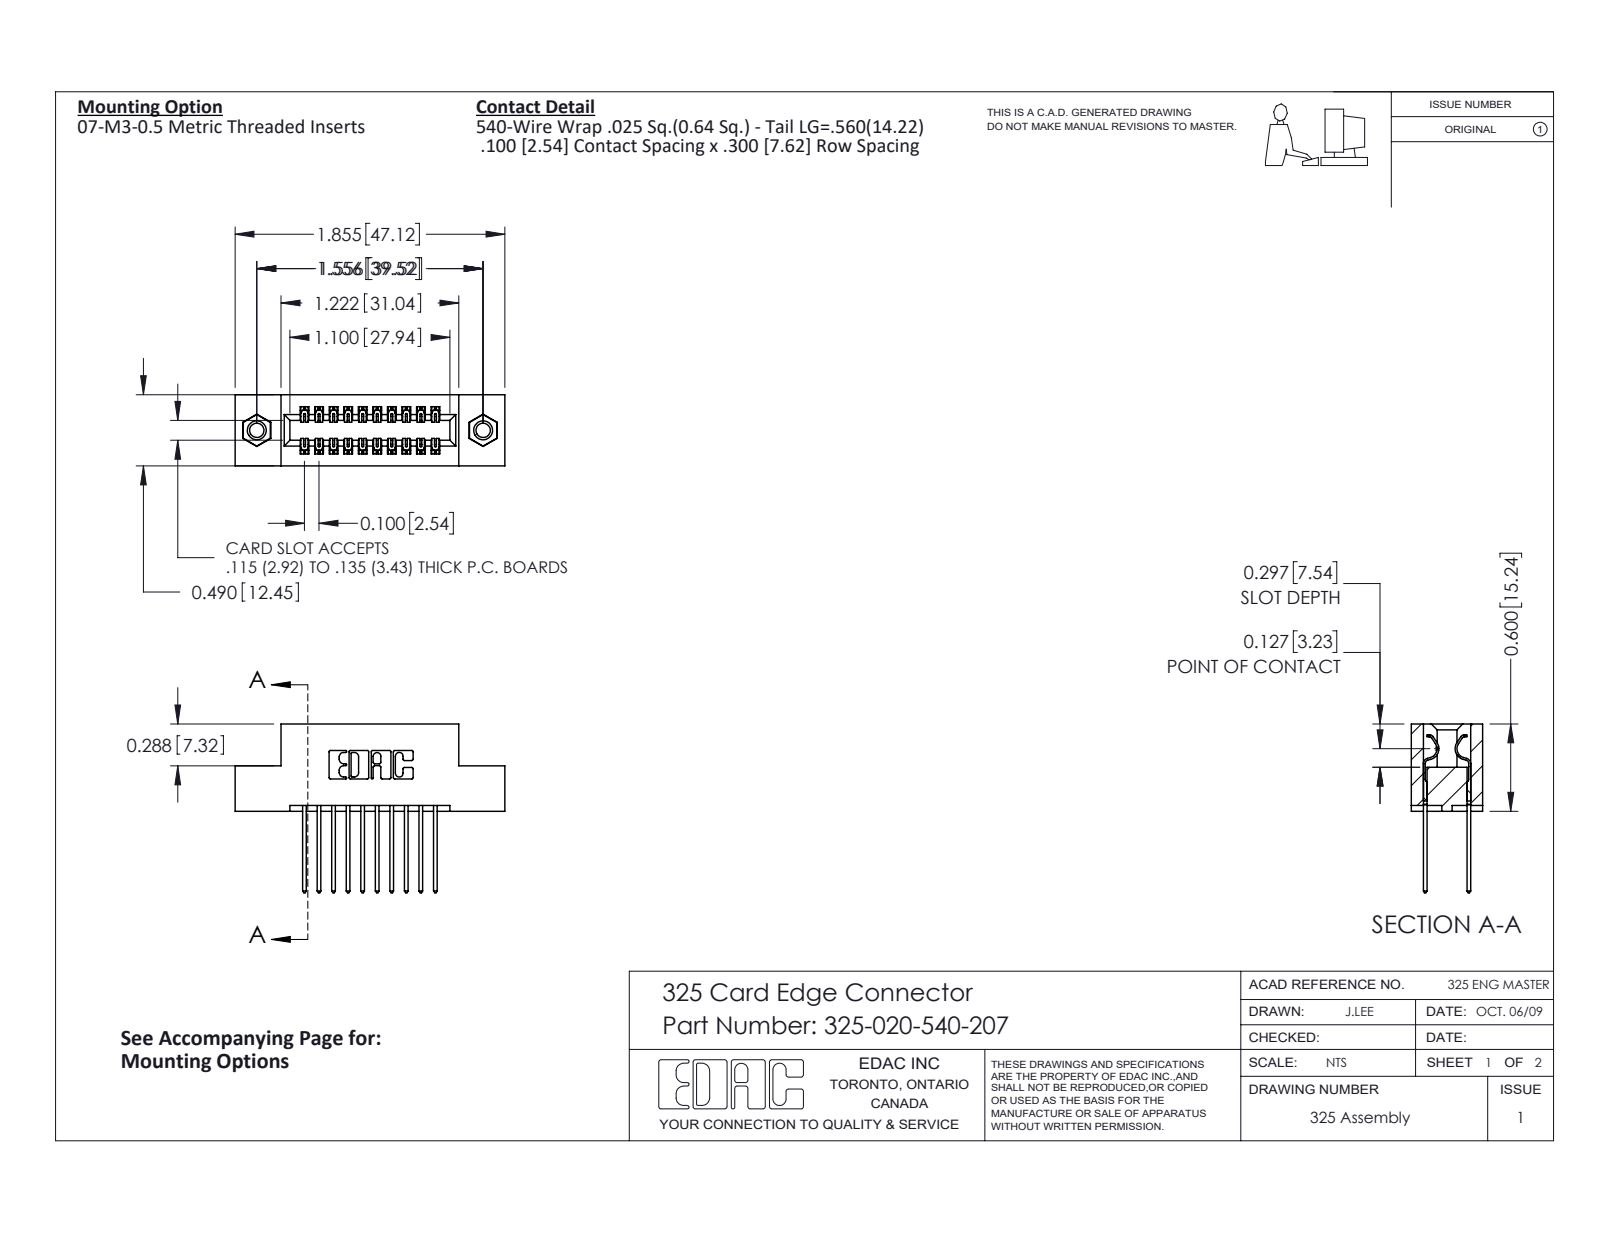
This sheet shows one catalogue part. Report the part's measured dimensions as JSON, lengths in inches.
{"part_name": "345-250-001_345-250-005-103; 325-292-001_325-293-140; 325-020-540-207; 325 Part_TI", "step_written_by": "SolidWorks 2016 (CONFIG_CONTROL_DESIGN)", "units": "inches", "bodies": {"solids": 23, "faces": 1214, "planar": 822, "cylindrical": 376, "other": 16}, "overall_size": [1.855, 1.16, 0.49], "volume_in3": 0.357, "surface_area_in2": 10.41, "round_holes": [[0.098, 2], [0.125, 2], [0.16, 2]], "round_bosses_or_shafts": [[0.155, 2]], "partial_cylinders_radius": [[0.006, 30], [0.01, 22], [0.01, 20], [0.007, 6], [0.031, 6], [0.026, 3], [0.014, 2], [0.022, 2]], "face_to_face_distances": [0.3, 0.083, 0.407, 0.49, 0.04, 0.1, 0.107, 0.383, 0.025, 0.2], "hole_center_spacings": [1.556]}
